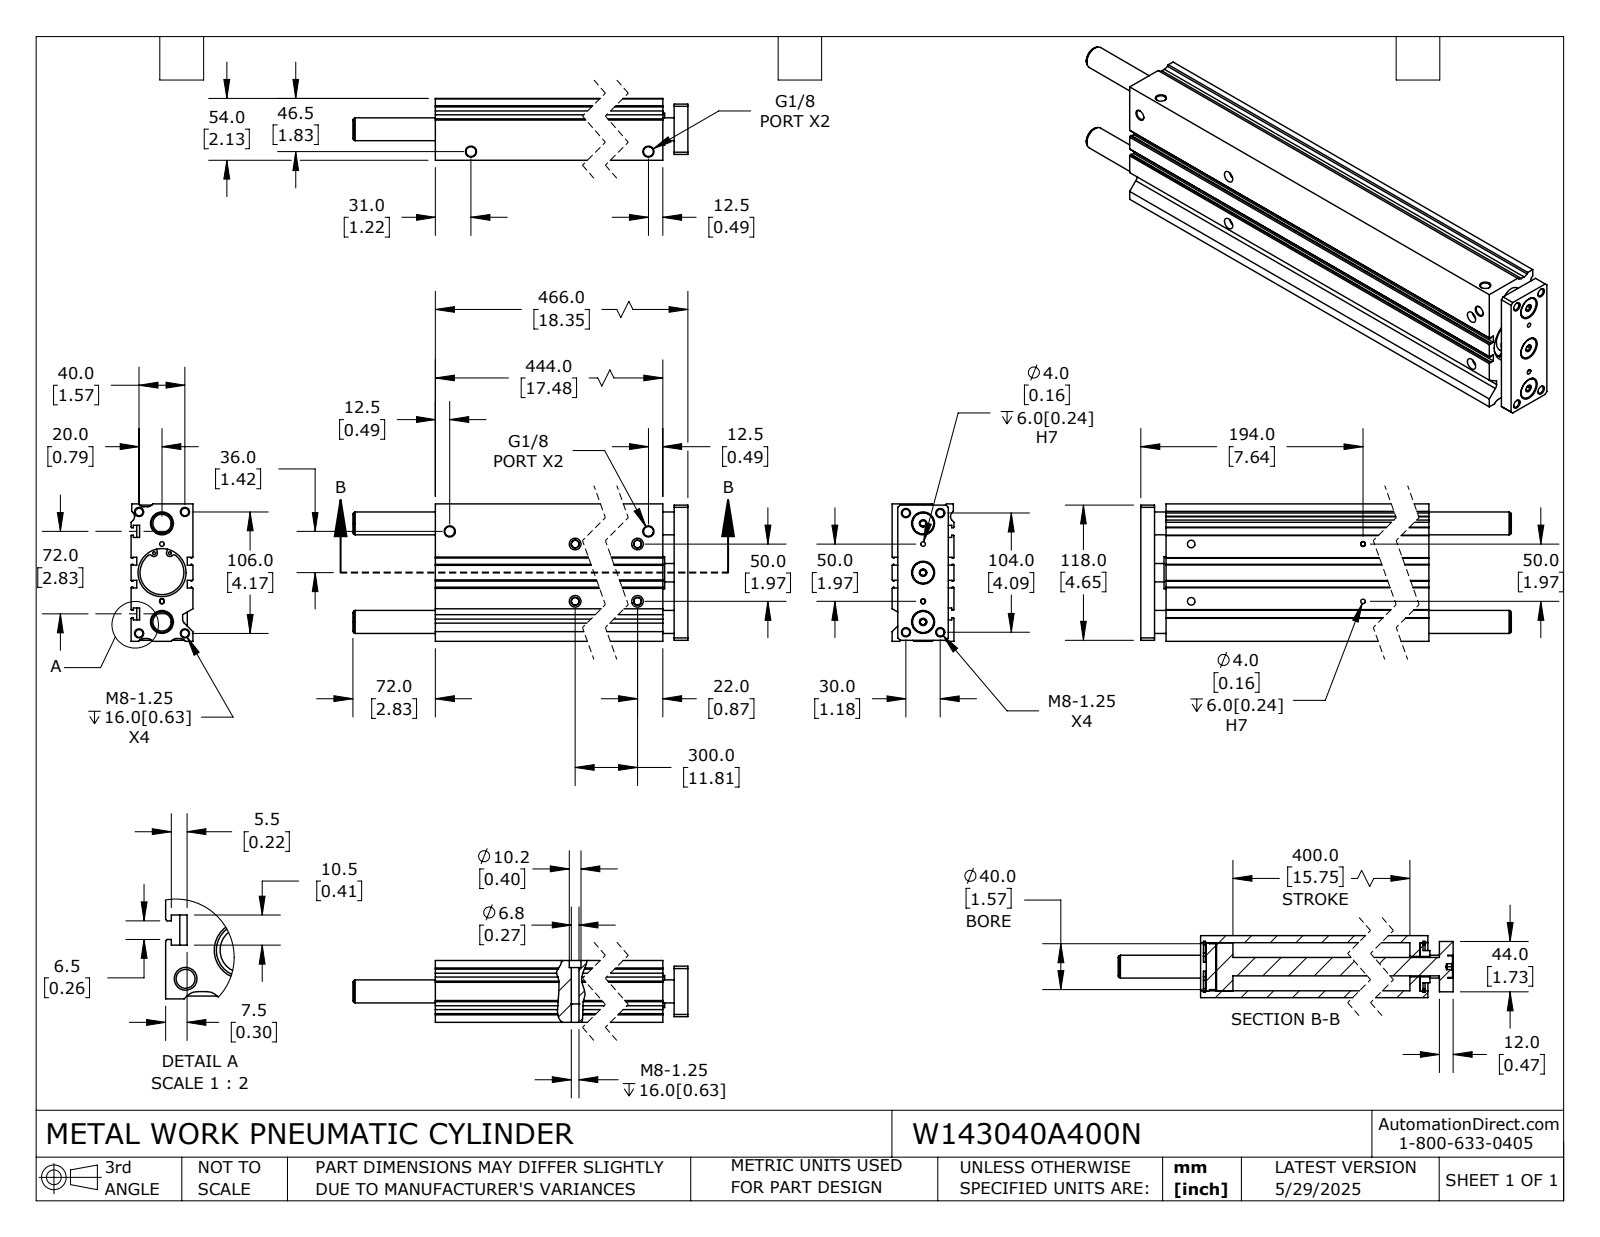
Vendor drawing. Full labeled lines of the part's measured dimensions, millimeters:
Part name (STEP PRODUCT): W143040A400N_BODY; W143040A400N_ROD; W143040A400N
STEP written by: SolidWorks 2024 (CONFIG_CONTROL_DESIGN)
Units: millimetres
Bodies: 6 solids, 393 faces (192 planar, 151 cylindrical, 50 other)
Overall size (bounding box): 538 × 120 × 54
Volume: 2 281 000 mm³ · Surface area: 452 100 mm²
Round holes (diameter × count): ⌀6.7 ×10, ⌀2.5 ×4, ⌀4 ×4, ⌀6.8 ×4, ⌀8.6 ×4, ⌀10.2 ×4, ⌀5 ×3, ⌀20 ×3, ⌀6.7 ×2, ⌀17.7 ×1, ⌀38.4 ×1
Round bosses / shafts (diameter × count): ⌀19 ×3, ⌀44.5 ×2, ⌀42 ×1, ⌀40 ×1, ⌀28 ×1, ⌀16 ×1
Partial cylindrical surfaces — rounded edges, fillets, slot ends (radius × count): R5 ×7, R2 ×4, R2.3 ×4, R2.9 ×4, R4 ×2
Main face-to-face distances: 54, 5, 49, 2.5, 120, 7.5, 46.5, 41.5, 44, 72
Hole centre spacings: 5.1, 10.5, 17.5, 18.3, 22.4, 26.9, 30.9, 34.4
